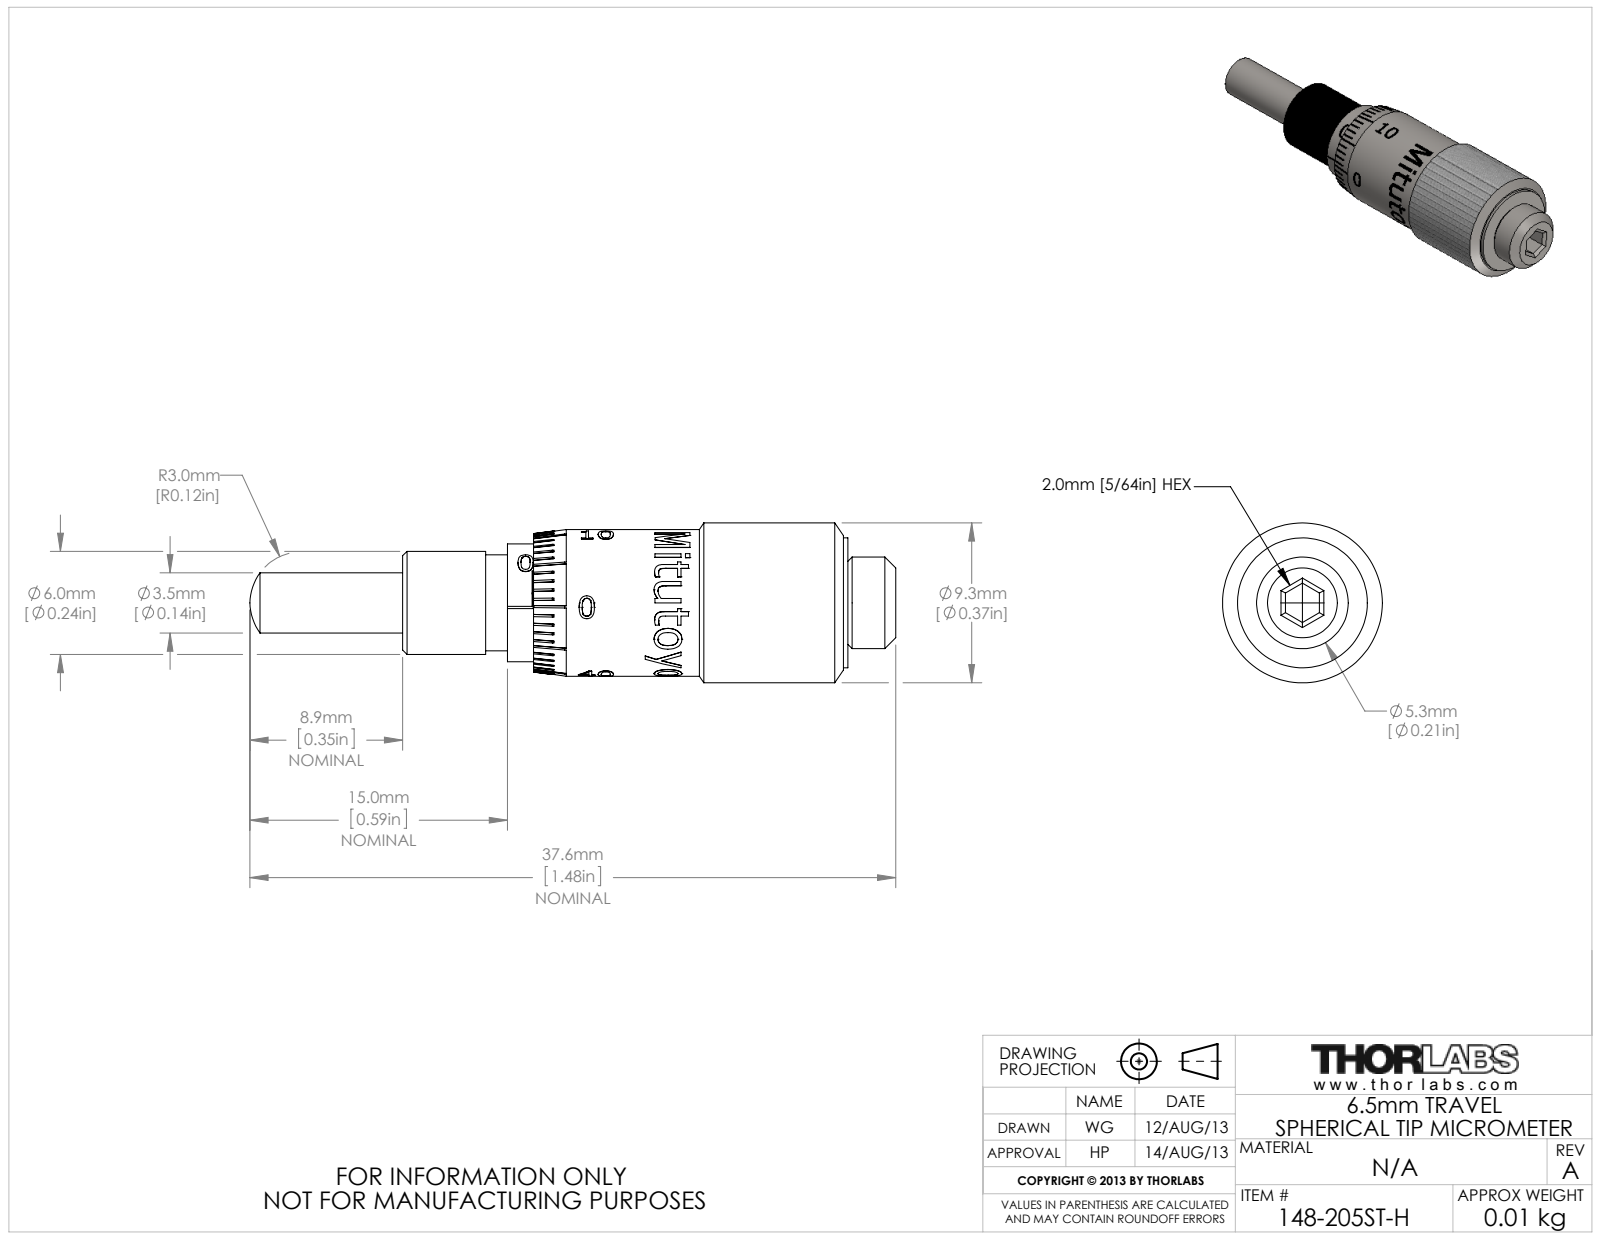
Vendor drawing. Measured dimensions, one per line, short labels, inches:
name: TTN017214-E0W
written by: SolidWorks 2012 (AUTOMOTIVE_DESIGN)
unit: in
bodies: 2 solids, 535 faces (226 planar, 91 cylindrical, 218 other)
size: 1.48 × 0.366 × 0.366
volume: 0.09 in³; area: 1.621 in²
holes: 1× ⌀0.091
bosses: 1× ⌀0.366, 1× ⌀0.336, 1× ⌀0.297, 1× ⌀0.27, 1× ⌀0.236, 1× ⌀0.22, 1× ⌀0.21, 1× ⌀0.138
rounds: 1× R0.135, 1× R0.164, 1× R0.168, 1× R0.169
face distances: 1.02, 0.3, 0.72, 0.24, 0.06, 0.78, 0.11, 0.83, 1.13, 0.89
